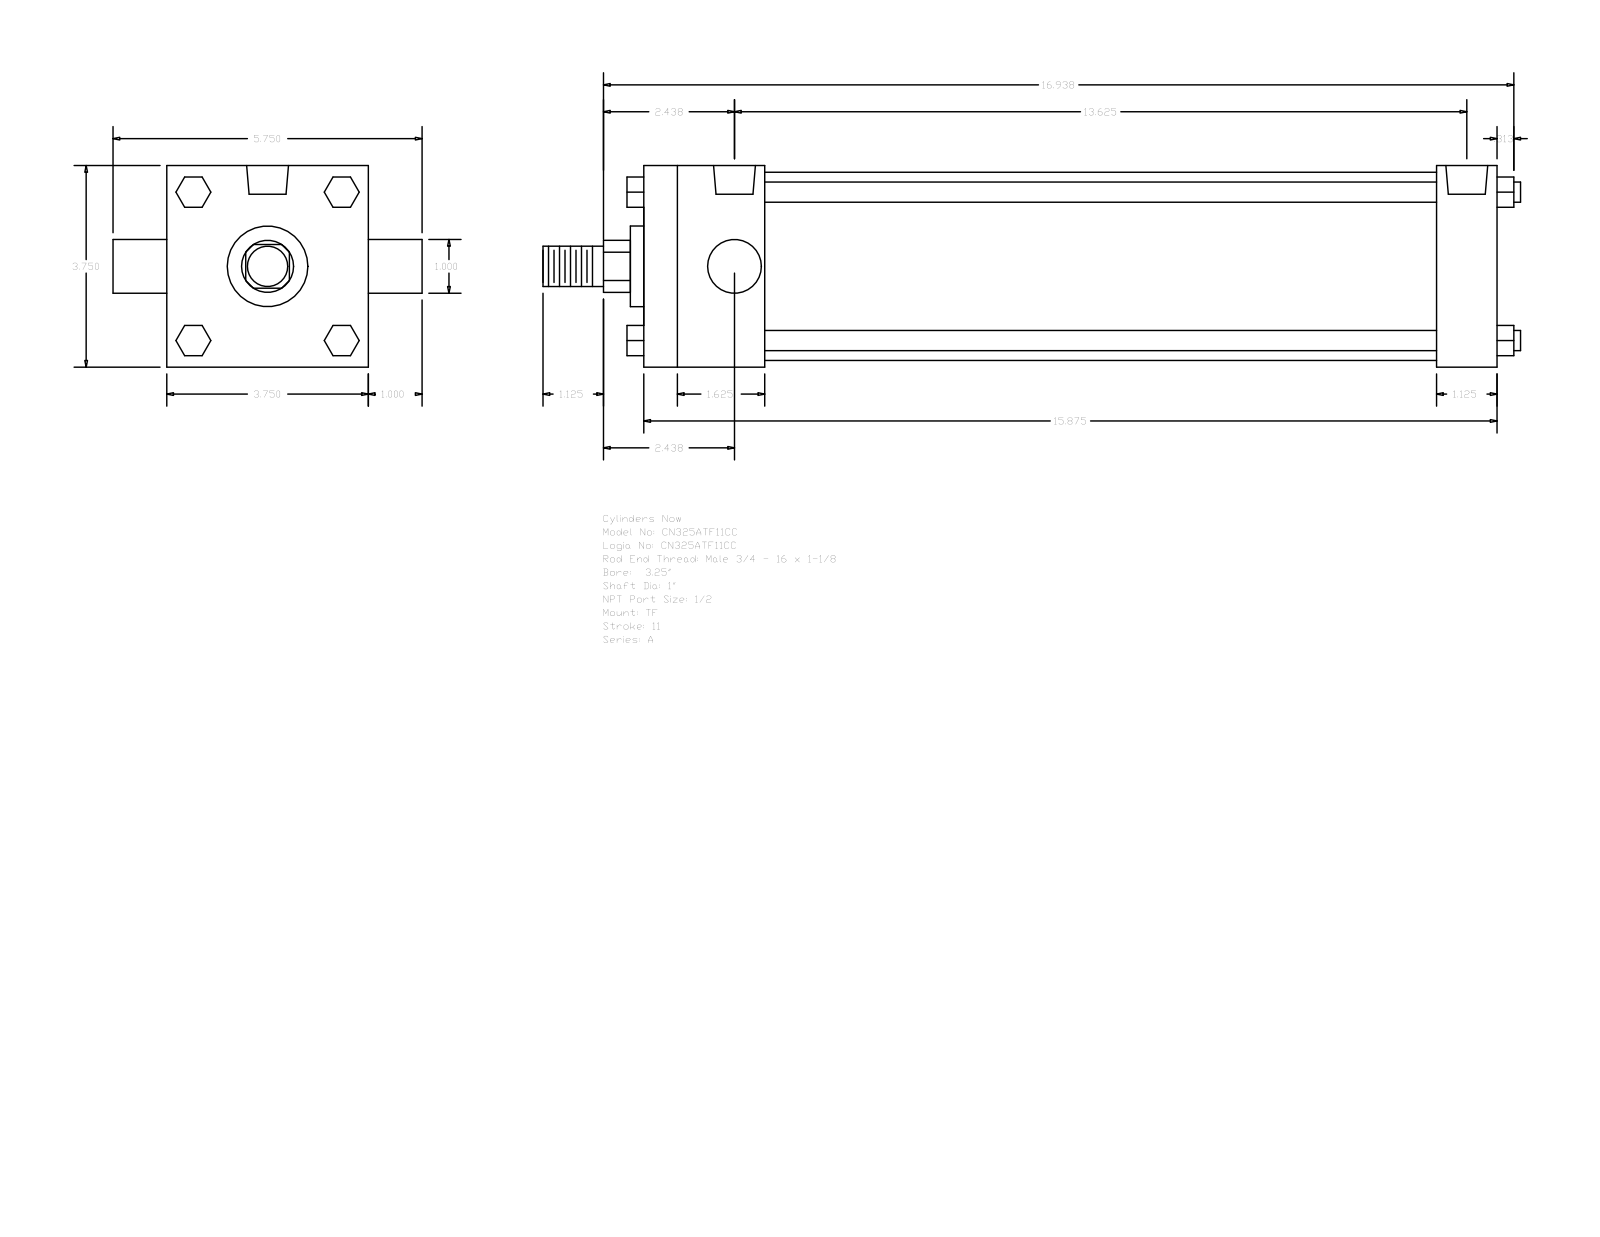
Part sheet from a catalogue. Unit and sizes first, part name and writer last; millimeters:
Units: millimetres
Overall size (bounding box): 461.96 × 146.05 × 95.25
Round holes (diameter × count): ⌀8.73 ×3, ⌀19.77 ×2
Round bosses / shafts (diameter × count): ⌀9.53 ×4, ⌀25.4 ×2, ⌀88.9 ×1, ⌀38.1 ×1, ⌀19.05 ×1
Partial cylindrical surfaces — rounded edges, fillets, slot ends (radius × count): R12.29 ×1
Main face-to-face distances: 95.24, 403.22, 28.57, 57.15, 374.65, 317.5, 346.07, 14.28, 35.05, 60.71
Hole centre spacings: 3.18, 342.9, 339.72, 346.08
Bodies: 0 solids, 120 faces (92 planar, 28 cylindrical, 0 other)
Part name (STEP PRODUCT): A_TF__0325_1
STEP written by: GSSL Pune (CONFIG_CONTROL_DESIGN)
